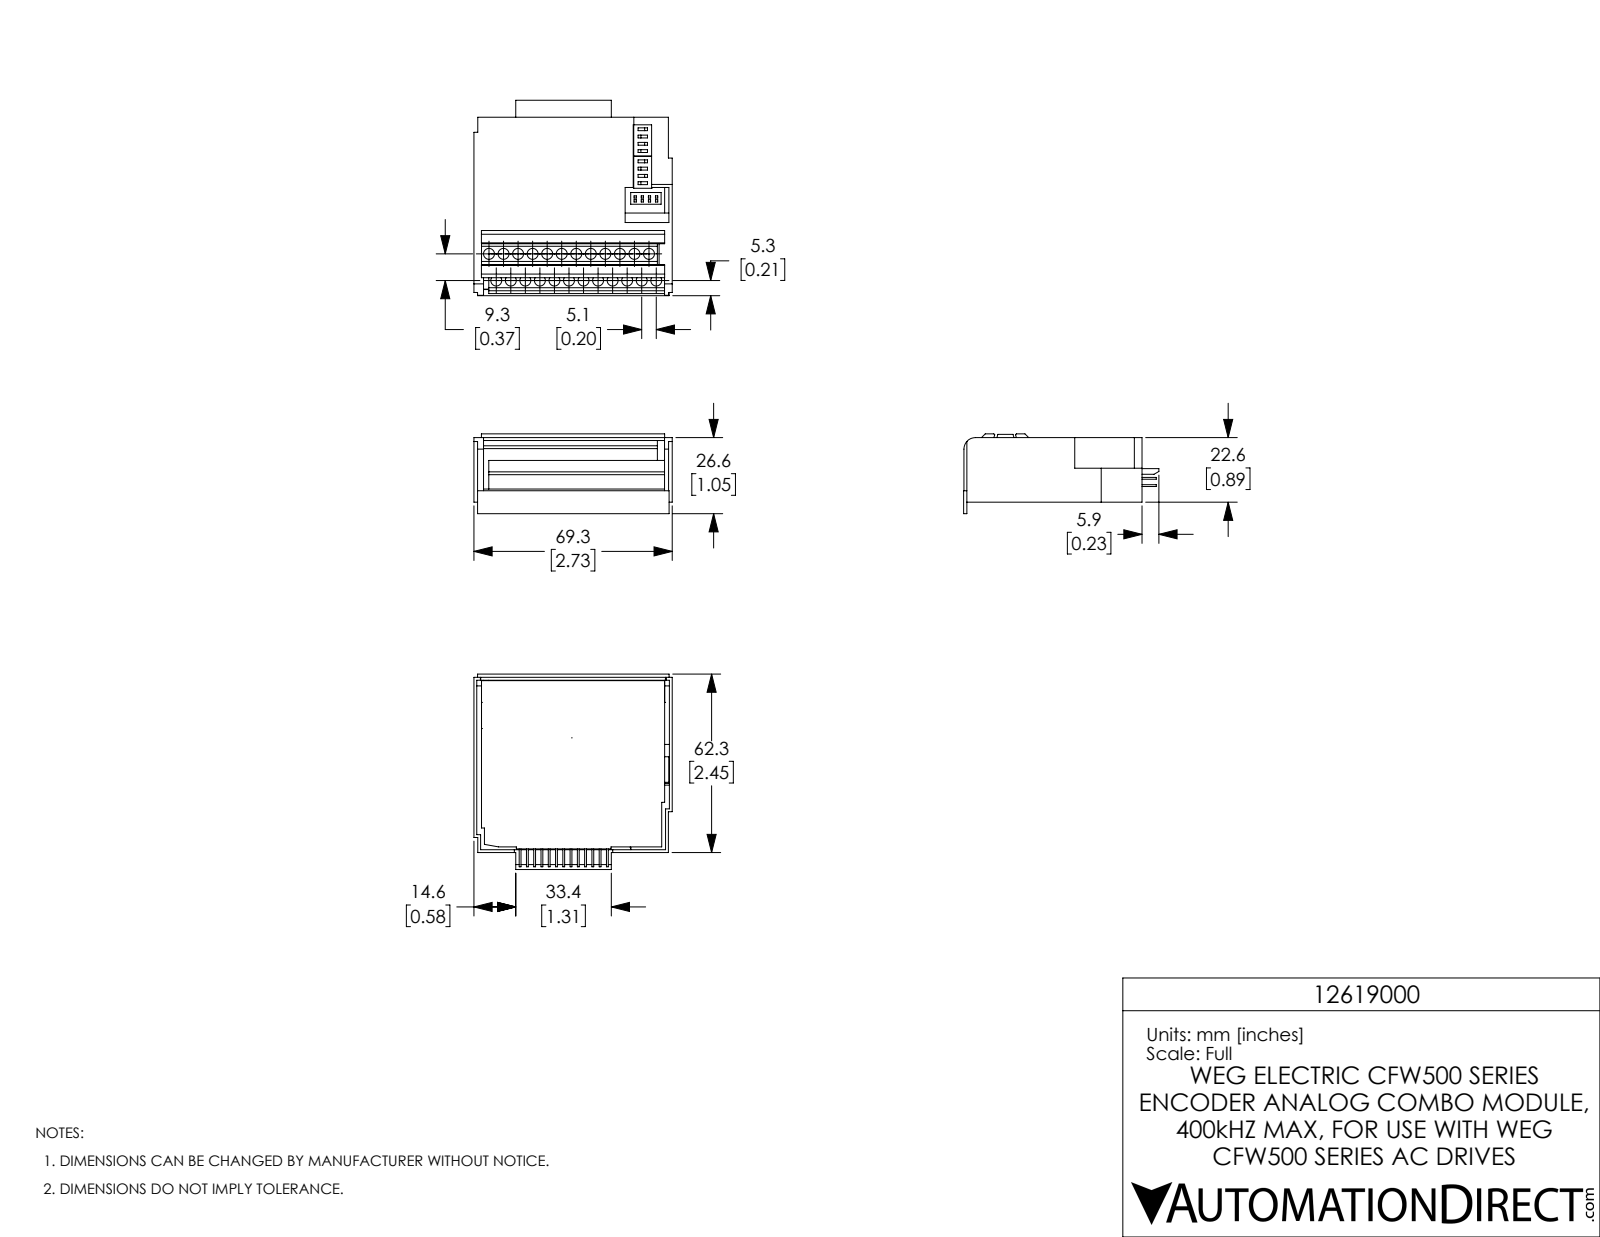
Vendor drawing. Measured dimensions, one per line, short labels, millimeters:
name: 12619000_ MODULO ENTRADA ENCODER CFW500_ENC Coord nc
written by: SolidWorks 2017 (AUTOMOTIVE_DESIGN)
unit: mm
bodies: 1 solid, 478 faces (426 planar, 52 cylindrical, 0 other)
size: 69.2 × 68.2 × 27.8
volume: 31 450 mm³; area: 30 270 mm²
holes: 24× ⌀3.8
rounds: 1× R3, 1× R4
face distances: 1, 18.5, 19.6, 1.6, 16.9, 18, 68.2, 69.3, 1.3, 43.3
hole spacings: 9.7, 5.1, 12, 10.2, 15.7, 15.2, 20.1, 20.3
